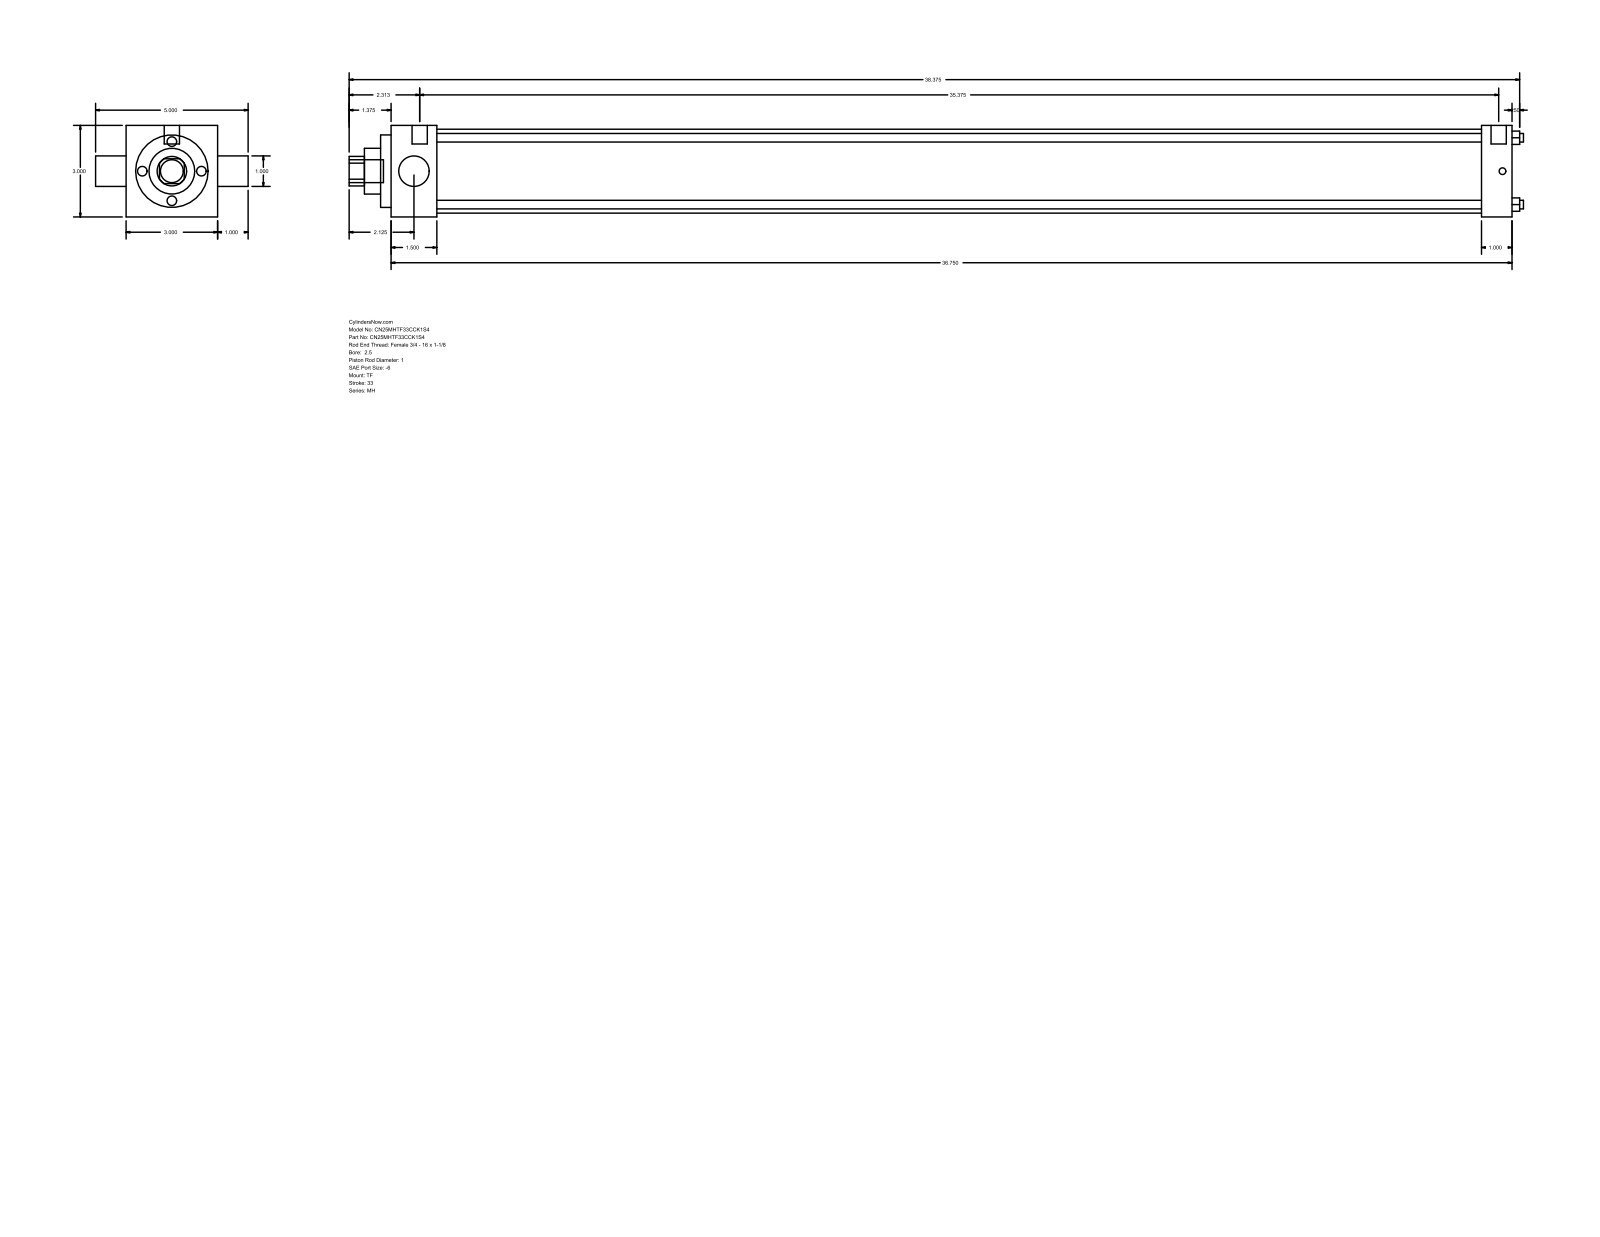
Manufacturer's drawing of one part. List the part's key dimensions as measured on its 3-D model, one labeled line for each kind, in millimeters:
Part name (STEP PRODUCT): MH_TF__0250_1
STEP written by: GSSL Pune (CONFIG_CONTROL_DESIGN)
Units: millimetres
Bodies: 0 solids, 86 faces (61 planar, 25 cylindrical, 0 other)
Overall size (bounding box): 977.9 × 127 × 76.2
Round holes (diameter × count): ⌀7.14 ×4, ⌀25.4 ×2, ⌀38.1 ×1, ⌀60.33 ×1, ⌀69.85 ×1
Round bosses / shafts (diameter × count): ⌀5.56 ×3, ⌀12.7 ×2, ⌀19.05 ×1
Partial cylindrical surfaces — rounded edges, fillets, slot ends (radius × count): R12.29 ×1
Main face-to-face distances: 76.2, 933.46, 25.4, 38.11, 895.35, 908.06, 869.95, 8.73, 46.84, 916.79
Hole centre spacings: 39.33, 55.62, 78.66
